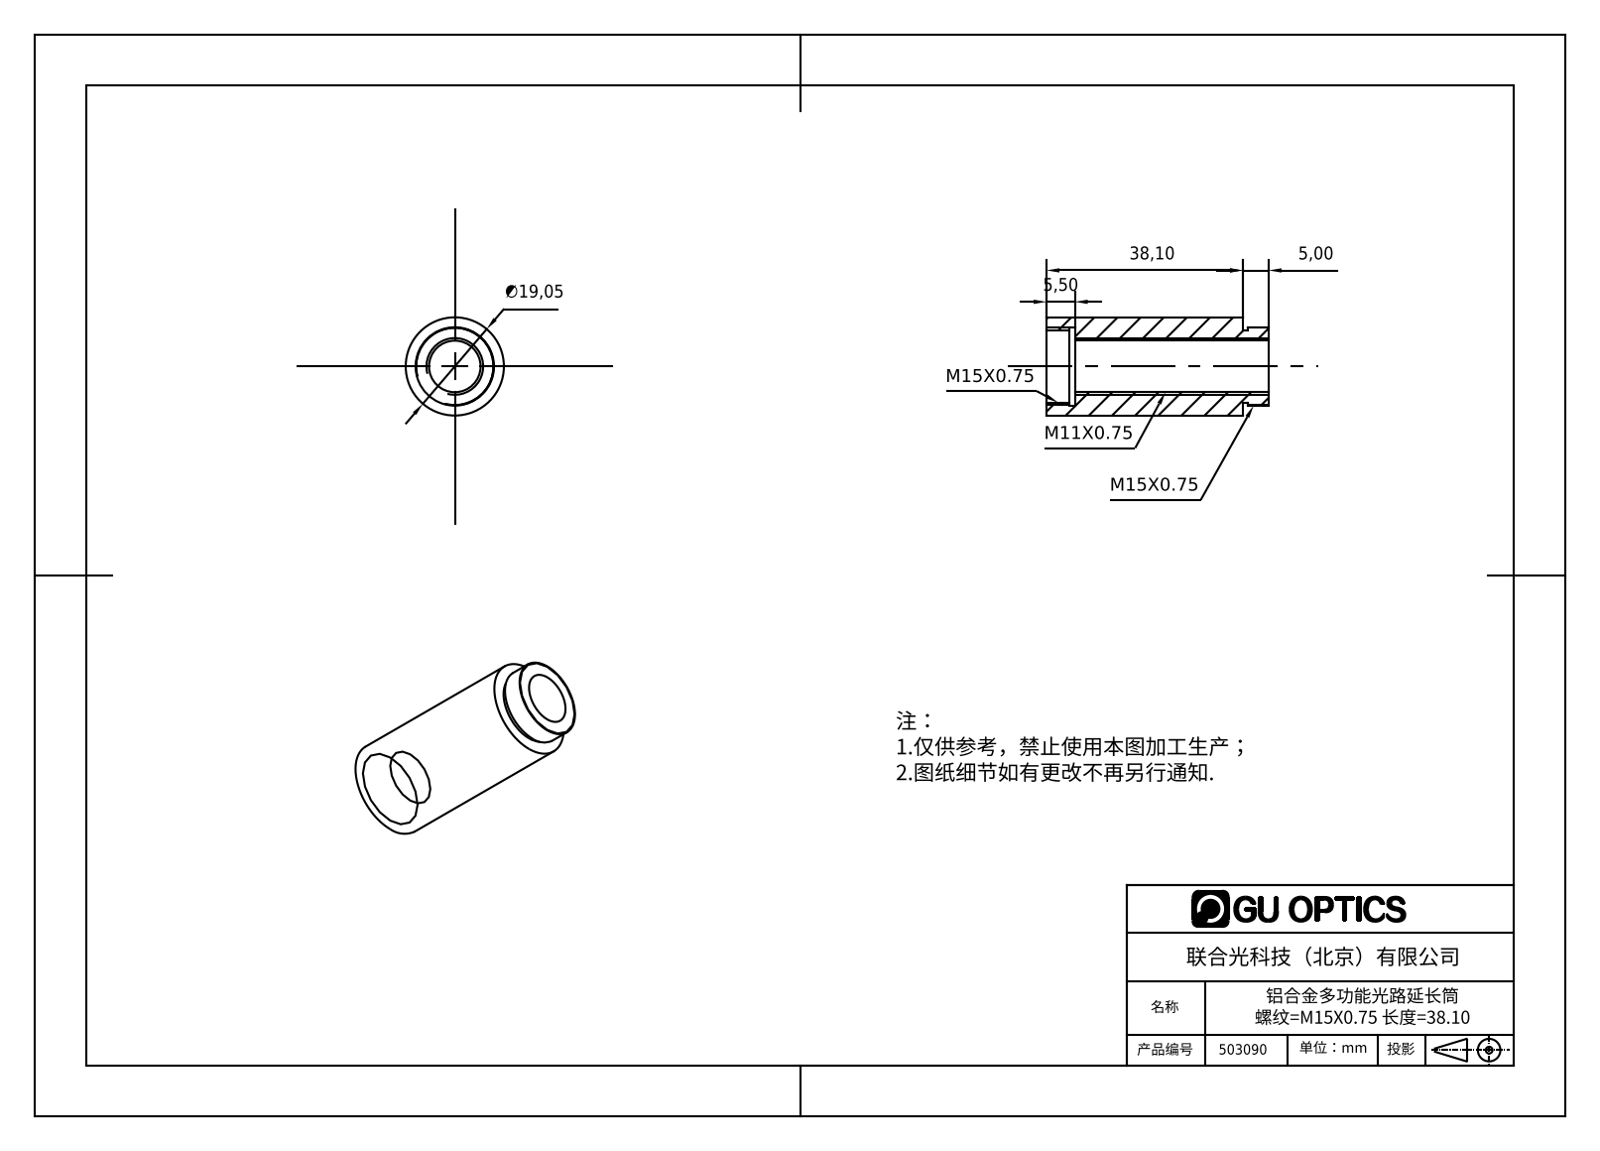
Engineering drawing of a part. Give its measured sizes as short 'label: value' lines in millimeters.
name: 503090
written by: SolidWorks 2016 (AUTOMOTIVE_DESIGN)
unit: mm
bodies: 1 solid, 18 faces (6 planar, 12 cylindrical, 0 other)
size: 43.1 × 19.05 × 19.05
volume: 7 912 mm³; area: 4 465 mm²
holes: 1× ⌀10, 1× ⌀14, 1× ⌀15.2
bosses: 1× ⌀19.05
face distances: 38.1, 5.5, 32.6, 43.1, 37.6, 5, 1, 33.6, 39.1, 4
